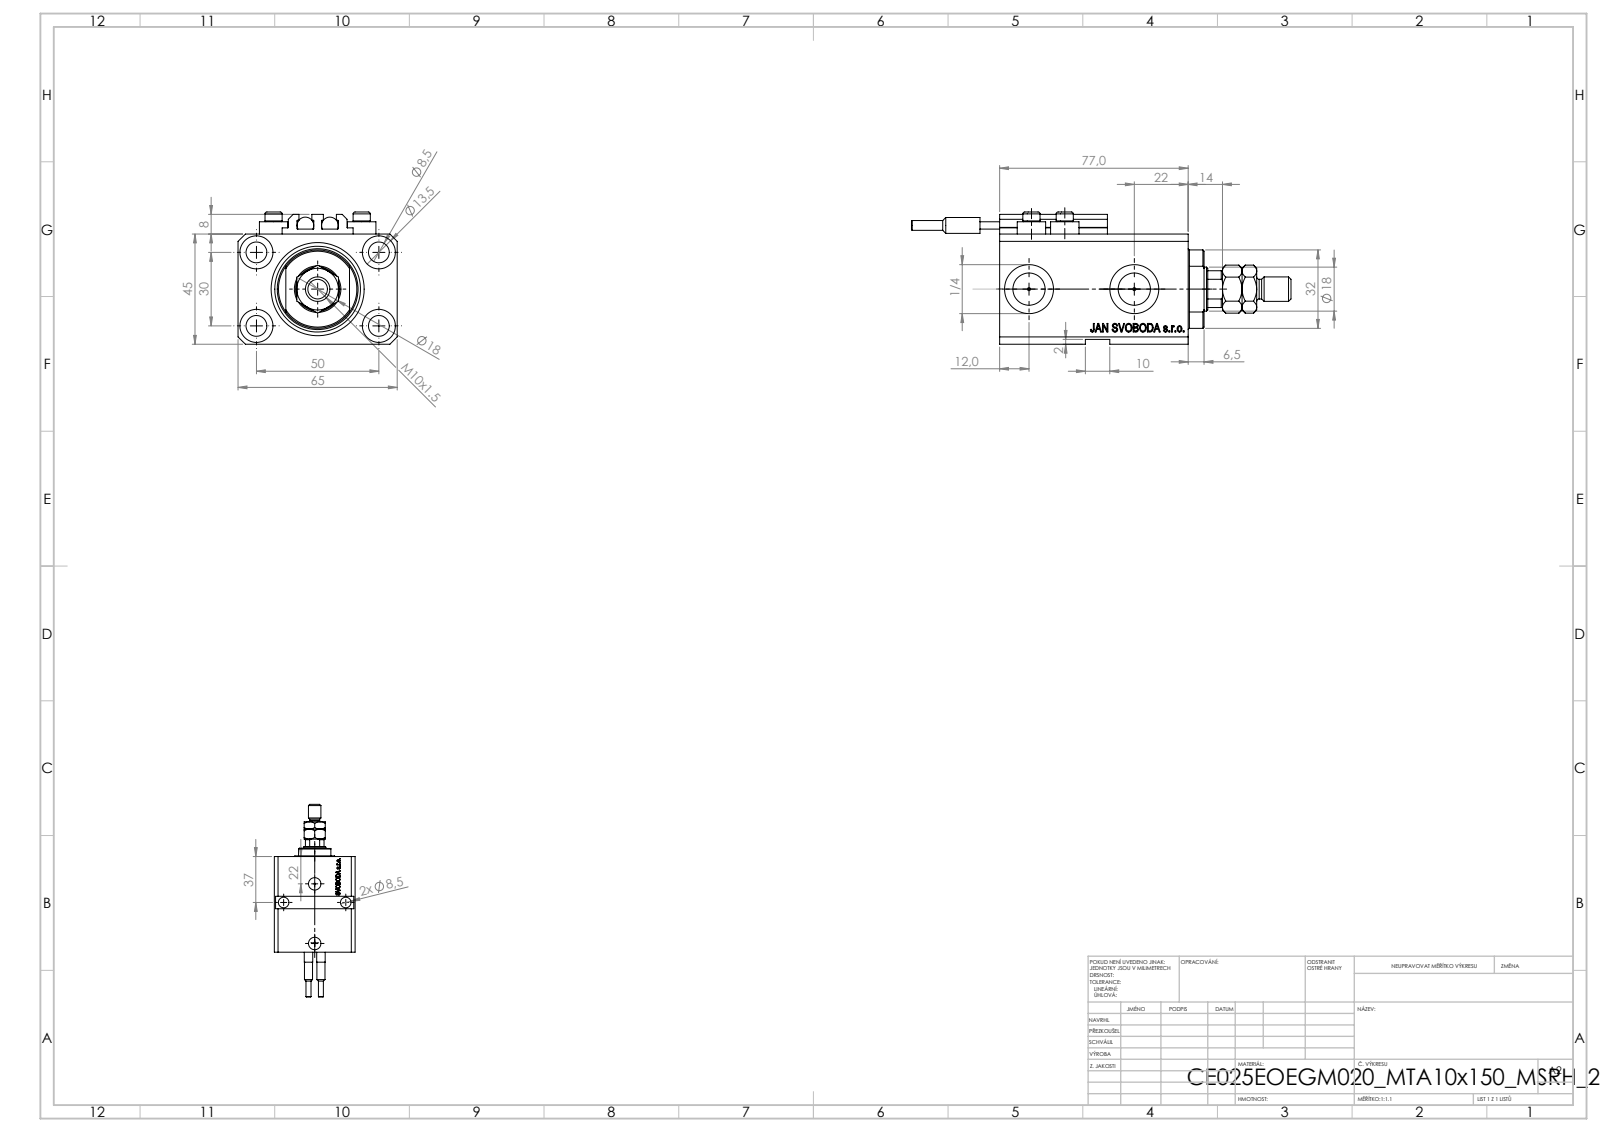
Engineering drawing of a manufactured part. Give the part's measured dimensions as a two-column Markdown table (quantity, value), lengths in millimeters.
| quantity | value |
| --- | --- |
| part name | MTA; V250CE_E_Body; SWITCH_V250CE; V250CE_C_VCP (+2 more) |
| STEP written by | SolidWorks 2019 (CONFIG_CONTROL_DESIGN) |
| units | millimeters |
| bodies | 11 solids, 1168 faces (558 planar, 142 cylindrical, 468 other) |
| overall size | 155 × 65 × 54 |
| volume | 207 834 mm³ |
| surface area | 63 674 mm² |
| round holes (diameter × count) | 8.5 × 7, 1.25 × 4, 4 × 4, 13.5 × 4, 10 × 2, 13.16 × 2, 20 × 2, 18 × 1, 25 × 1, 38 × 1 |
| round bosses / shafts (diameter × count) | 11.6 × 4, 7 × 4, 6.8 × 2, 6.5 × 2, 4 × 2, 10 × 1, 8 × 1 |
| partial cylindrical surfaces (radius × count) | 0.2 × 10, 8.5 × 1, 16 × 1 |
| main face-to-face distances | 45, 65, 14, 63, 2, 3, 77, 6.9, 47, 5 |
| hole center spacings | 29.15, 50, 13.6, 15.12, 18.81, 18.97, 26.22, 26.61 |
